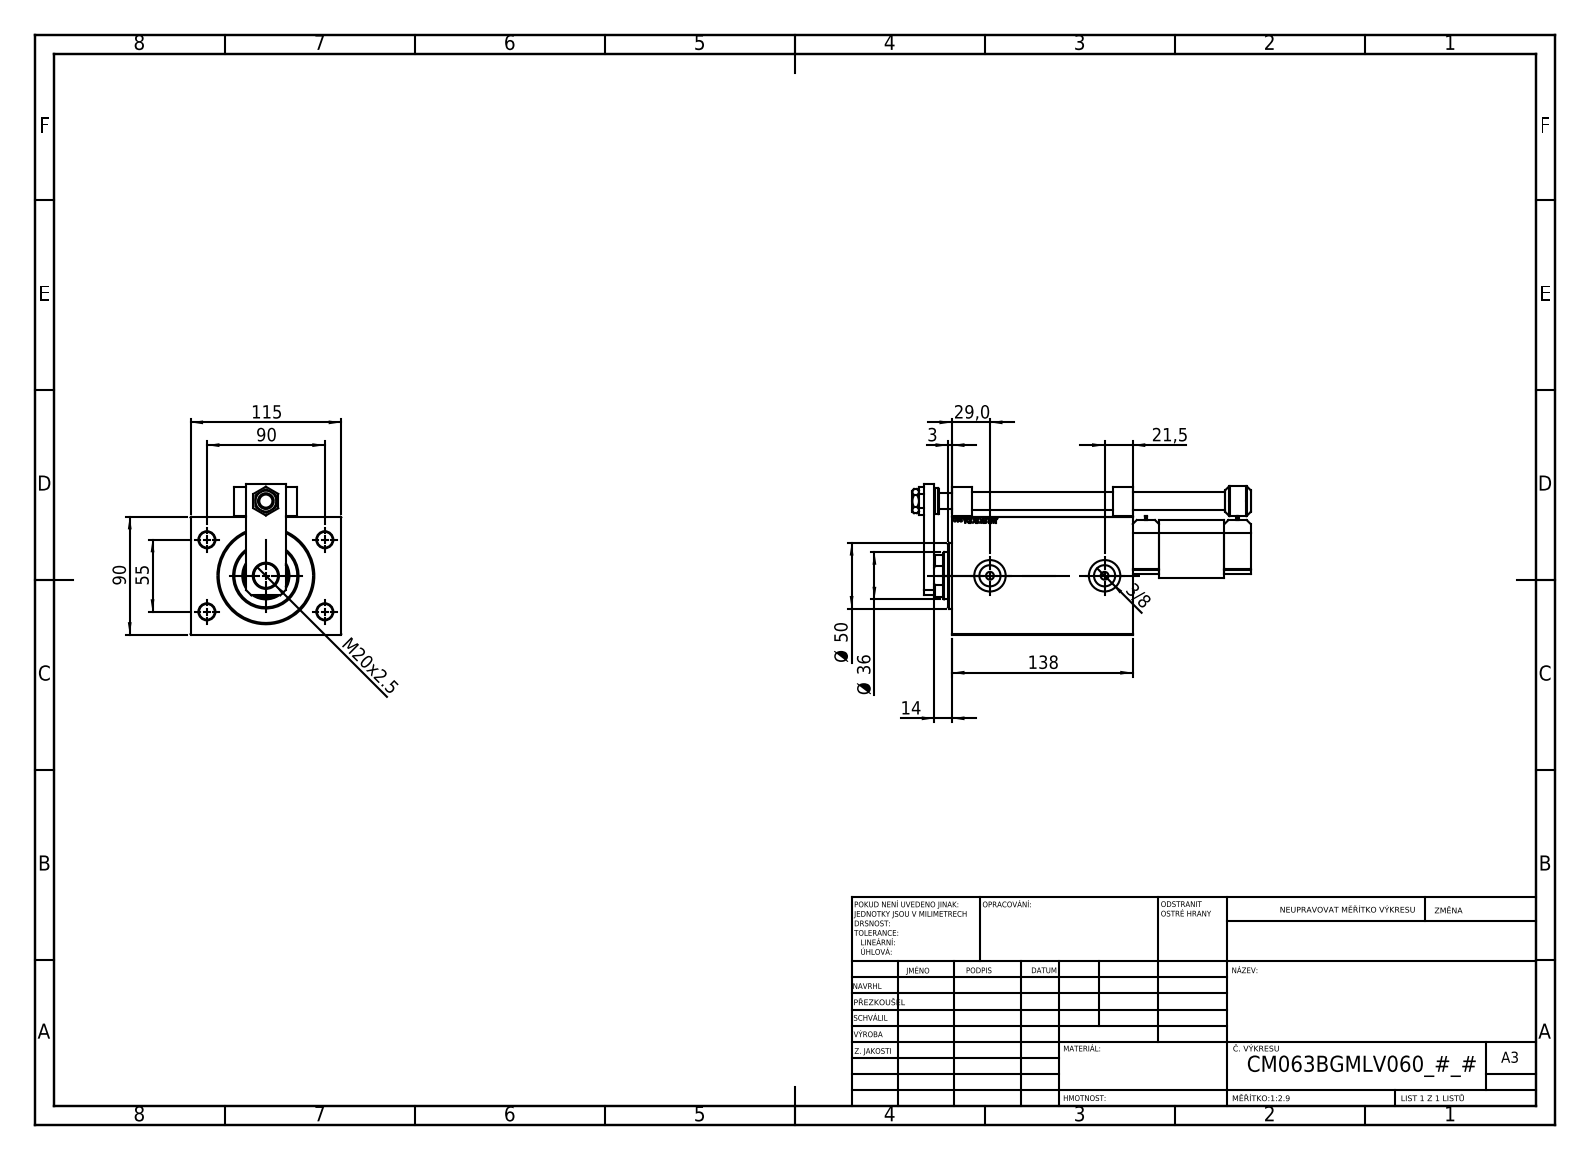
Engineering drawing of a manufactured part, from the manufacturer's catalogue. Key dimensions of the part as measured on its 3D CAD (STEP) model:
Part name (STEP PRODUCT): V450CM_B_VCP; SWITCH P; MIDDLE; V450CM_VC_B (+7 more)
STEP written by: SolidWorks 2019 (CONFIG_CONTROL_DESIGN)
Units: millimetres
Bodies: 14 solids, 1103 faces (512 planar, 110 cylindrical, 481 other)
Overall size (bounding box): 258.5 × 115 × 115
Volume: 1 520 000 mm³ · Surface area: 204 949 mm²
Round holes (diameter × count): ⌀12 ×5, ⌀4 ×4, ⌀8 ×4, ⌀6 ×2, ⌀16.17 ×2, ⌀24 ×2, ⌀13 ×1, ⌀14 ×1, ⌀18.5 ×1, ⌀20 ×1, ⌀36 ×1, ⌀63 ×1
Round bosses / shafts (diameter × count): ⌀20 ×3, ⌀16 ×2, ⌀14 ×2, ⌀6 ×2, ⌀50 ×1, ⌀23 ×1
Partial cylindrical surfaces — rounded edges, fillets, slot ends (radius × count): R3 ×1, R17.5 ×1
Main face-to-face distances: 90, 115, 138, 37.5, 17.5, 120.5, 13.5, 77.5, 20, 87.5
Hole centre spacings: 52.74, 20, 53.81, 55, 90, 95.74, 105.48, 123
